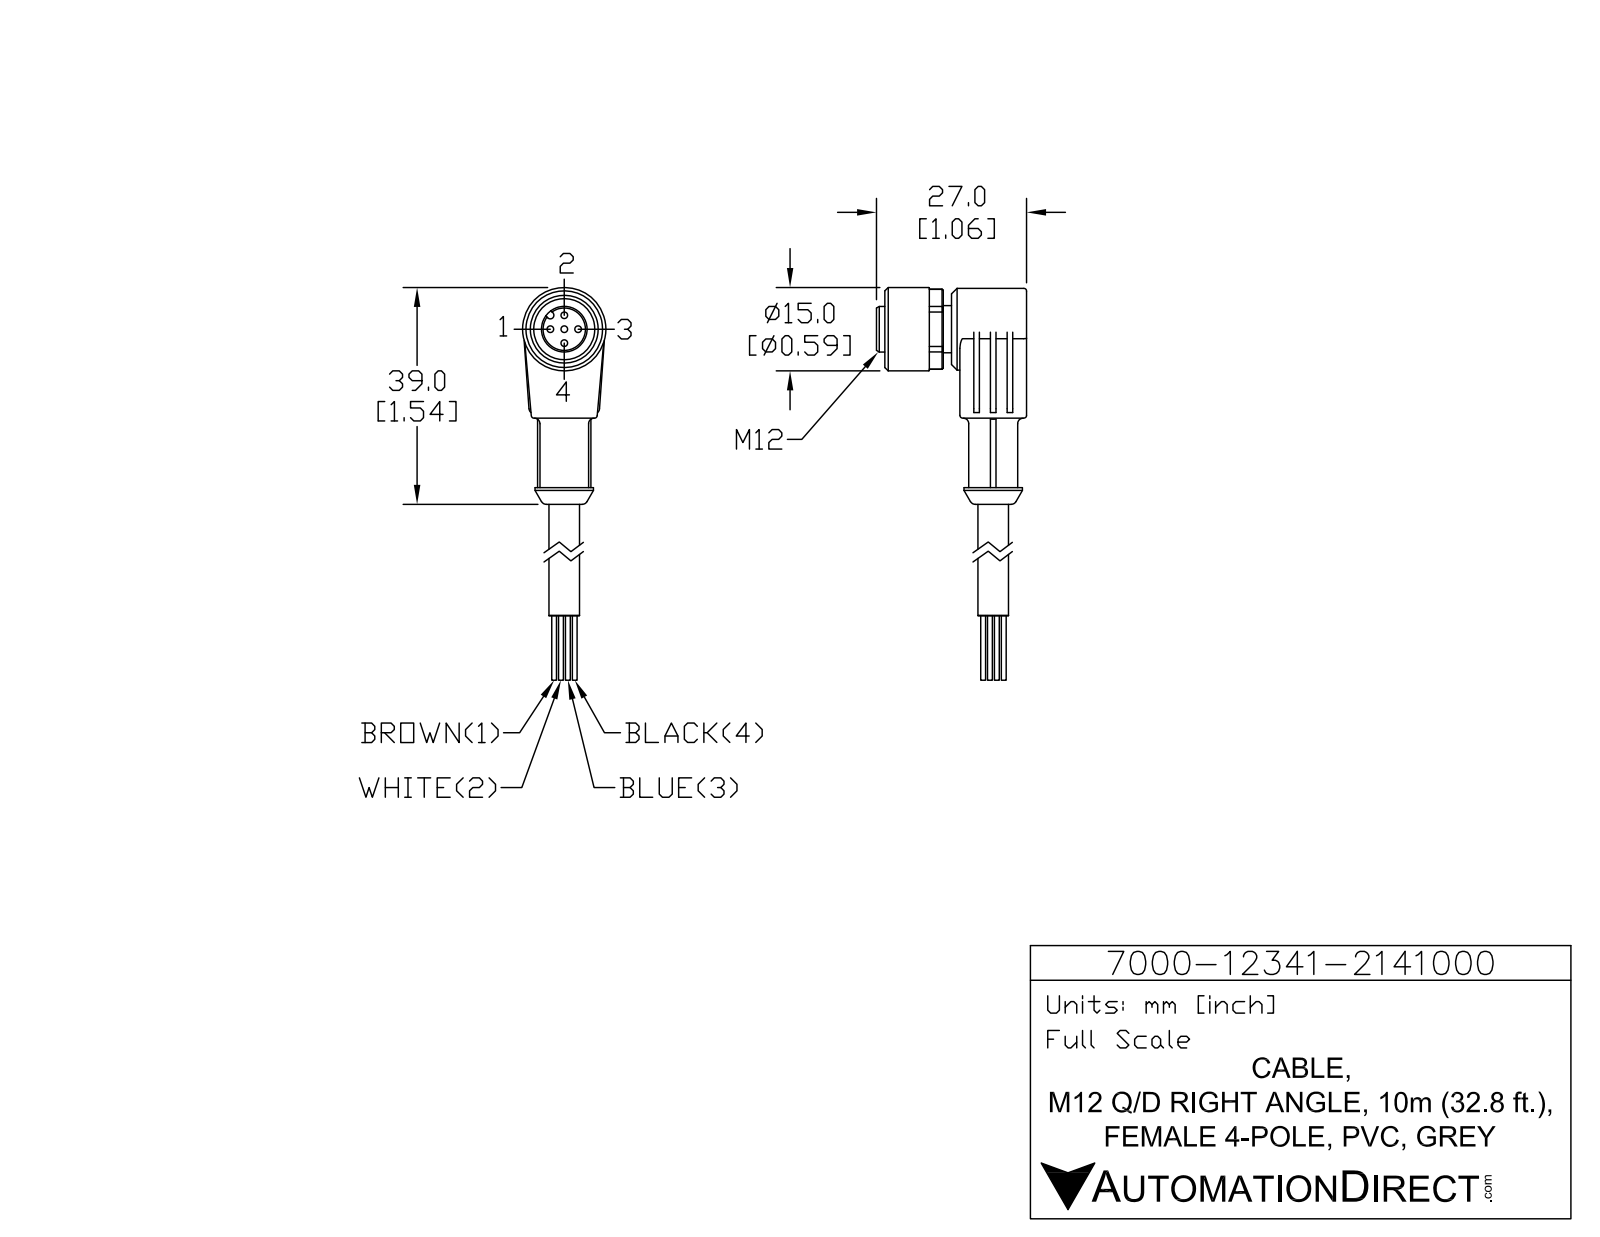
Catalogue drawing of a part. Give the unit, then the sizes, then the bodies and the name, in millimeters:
Units: millimetres
Overall size (bounding box): 59 × 27 × 15
Round holes (diameter × count): ⌀1.2 ×5, ⌀4.8 ×1, ⌀11 ×1
Round bosses / shafts (diameter × count): ⌀15 ×1, ⌀14.7 ×1, ⌀10.5 ×1, ⌀8.8 ×1, ⌀8.5 ×1, ⌀8.2 ×1, ⌀5.5 ×1
Partial cylindrical surfaces — rounded edges, fillets, slot ends (radius × count): R0.5 ×8, R1 ×2, R0.65 ×1, R7.2 ×1
Main face-to-face distances: 12, 1.5, 3, 13.5, 15, 5.5, 9.5, 6, 8, 12.5
Hole centre spacings: 2.5, 3.54, 5
Volume: 6 805 mm³ · Surface area: 3 613 mm²
Bodies: 1 solid, 150 faces (61 planar, 60 cylindrical, 29 other)
Part name (STEP PRODUCT): 7000-12341-2141000
STEP written by: SolidWorks 2015 (AUTOMOTIVE_DESIGN)
